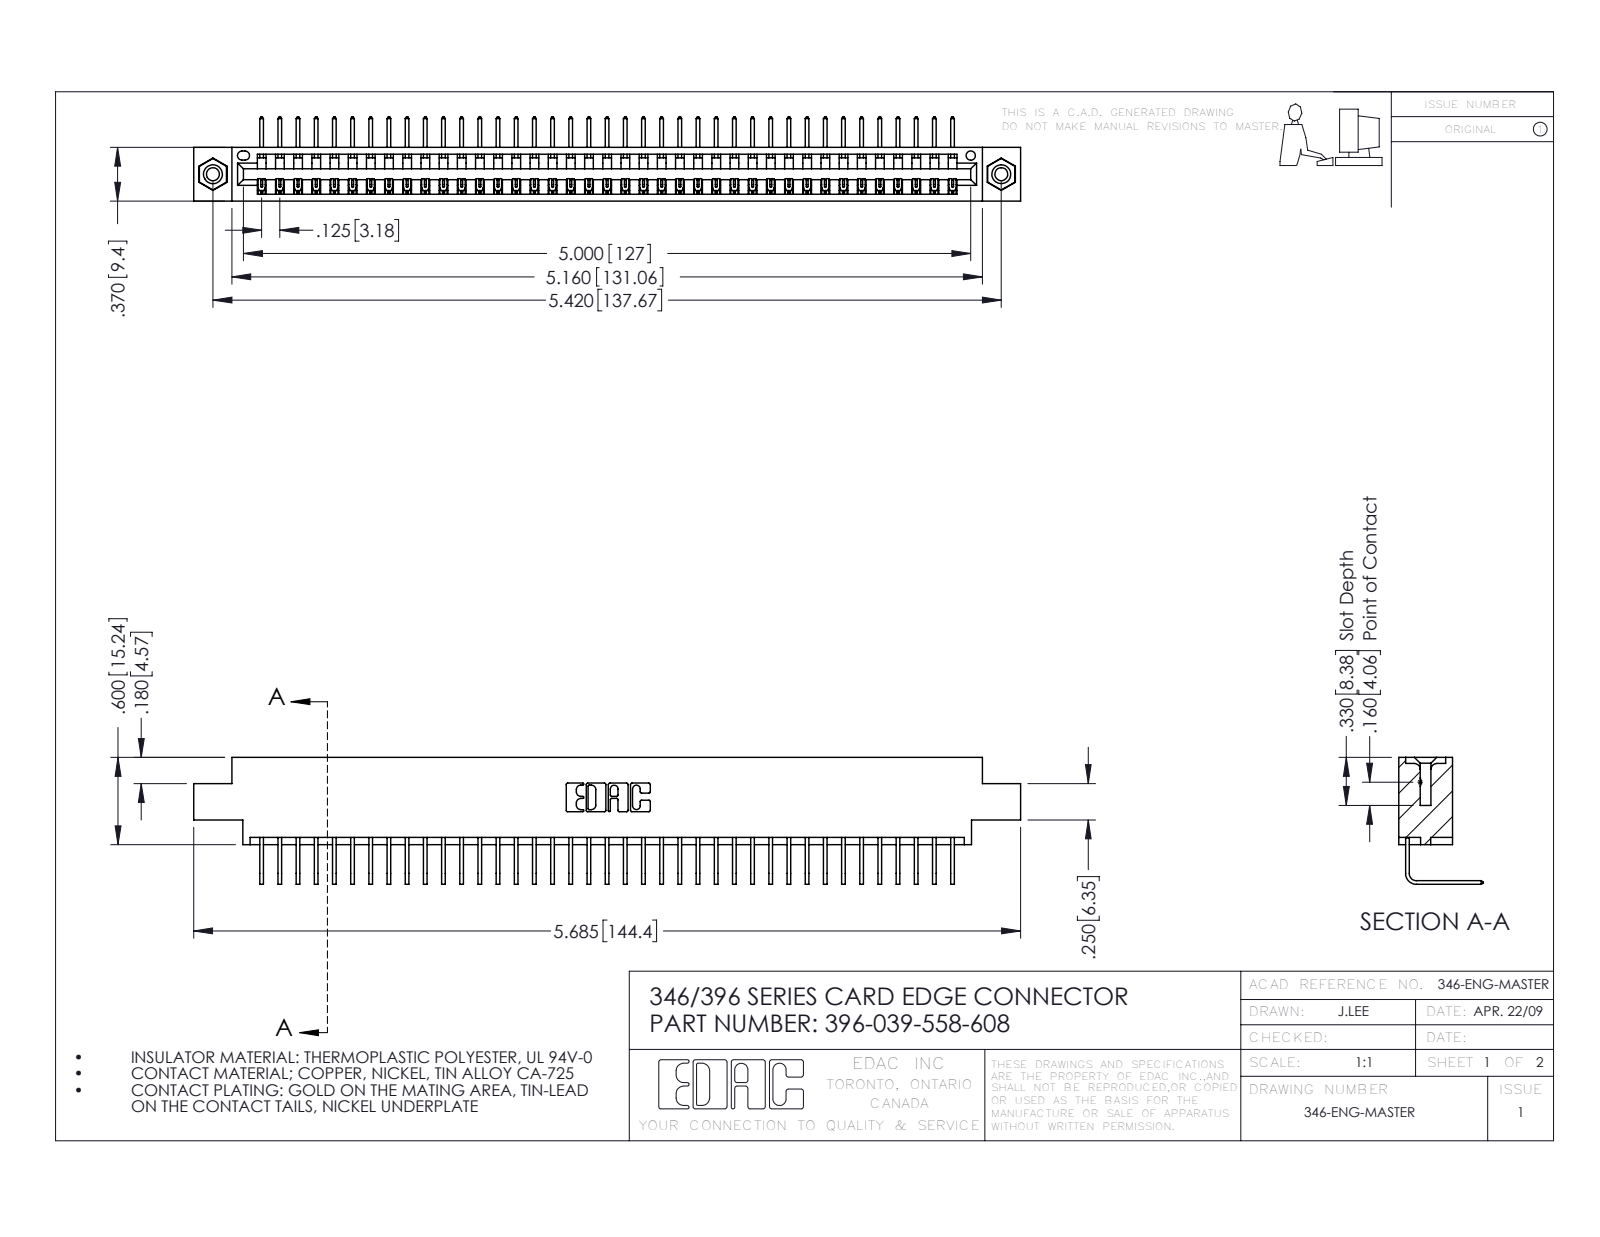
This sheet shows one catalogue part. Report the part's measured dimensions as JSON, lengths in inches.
{"part_name": "396-039-558-608; 345-250-001_345-250-003-102; 345-292-001_558 Tail - 2; 346 Part_0.170 Offset - 0.156 Dia-TI", "step_written_by": "SolidWorks 2016 (CONFIG_CONTROL_DESIGN)", "units": "inches", "bodies": {"solids": 42, "faces": 2526, "planar": 1750, "cylindrical": 760, "other": 16}, "overall_size": [5.685, 0.873, 0.58], "volume_in3": 0.84, "surface_area_in2": 28.11, "round_holes": [[0.089, 2], [0.125, 2], [0.156, 2], [0.064, 1]], "round_bosses_or_shafts": [[0.155, 2]], "partial_cylinders_radius": [[0.006, 78], [0.01, 22], [0.007, 6], [0.031, 6], [0.026, 3], [0.031, 2], [0.04, 2], [0.014, 1]], "face_to_face_distances": [0.322, 0.048, 0.37, 0.25, 0.298, 0.025, 0.072, 0.222, 0.148, 0.1], "hole_center_spacings": [0.246, 5.211, 5.42]}
